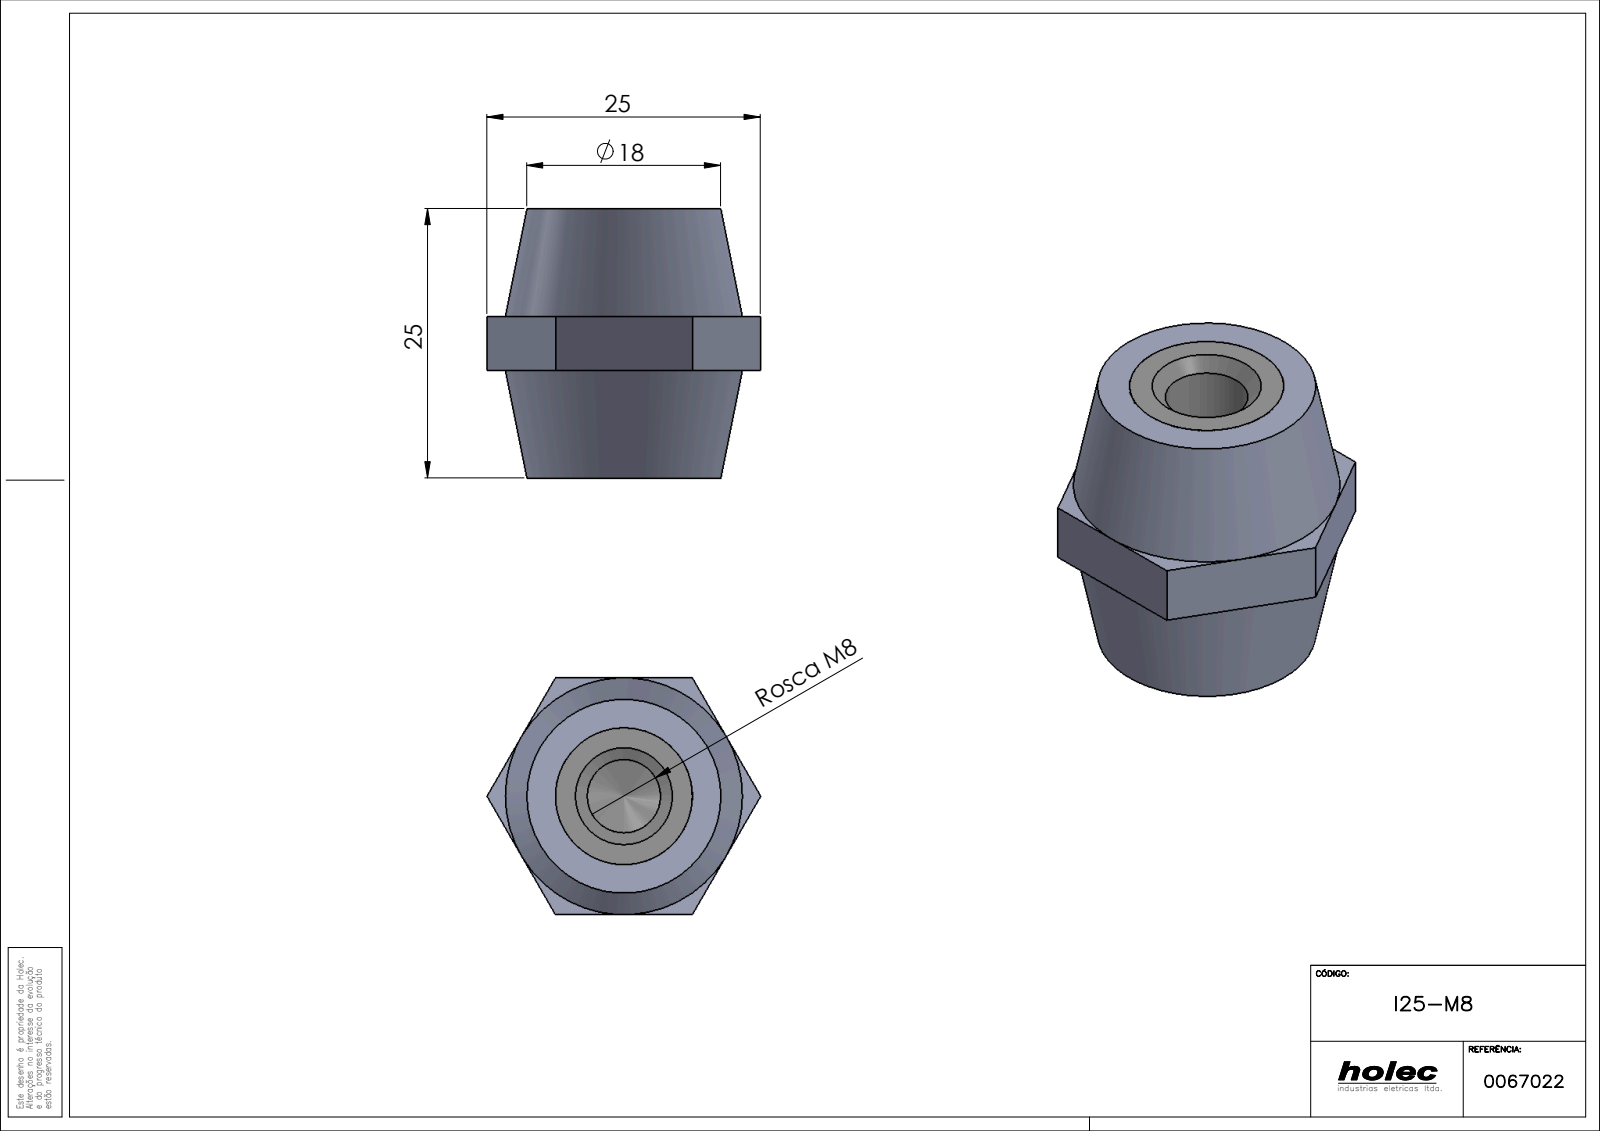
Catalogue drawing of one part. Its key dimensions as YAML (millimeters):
part_name: "I25-M8; PB1_0101(PB1_0101_08); PB1_0001"
step_written_by: "SolidWorks 2017 (AUTOMOTIVE_DESIGN)"
units: millimeters
bodies: {solids: 3, faces: 154, planar: 82, cylindrical: 12, other: 60}
overall_size: [25.4, 25, 22]
volume: 7782
surface_area: 5187
round_holes:
  - {diameter: 6.8, count: 1}
  - {diameter: 10, count: 1}
face_to_face_distances: [12.7, 15.01, 15, 3.5, 6.5, 10, 9.99, 5.01, 6.49, 8.51]
